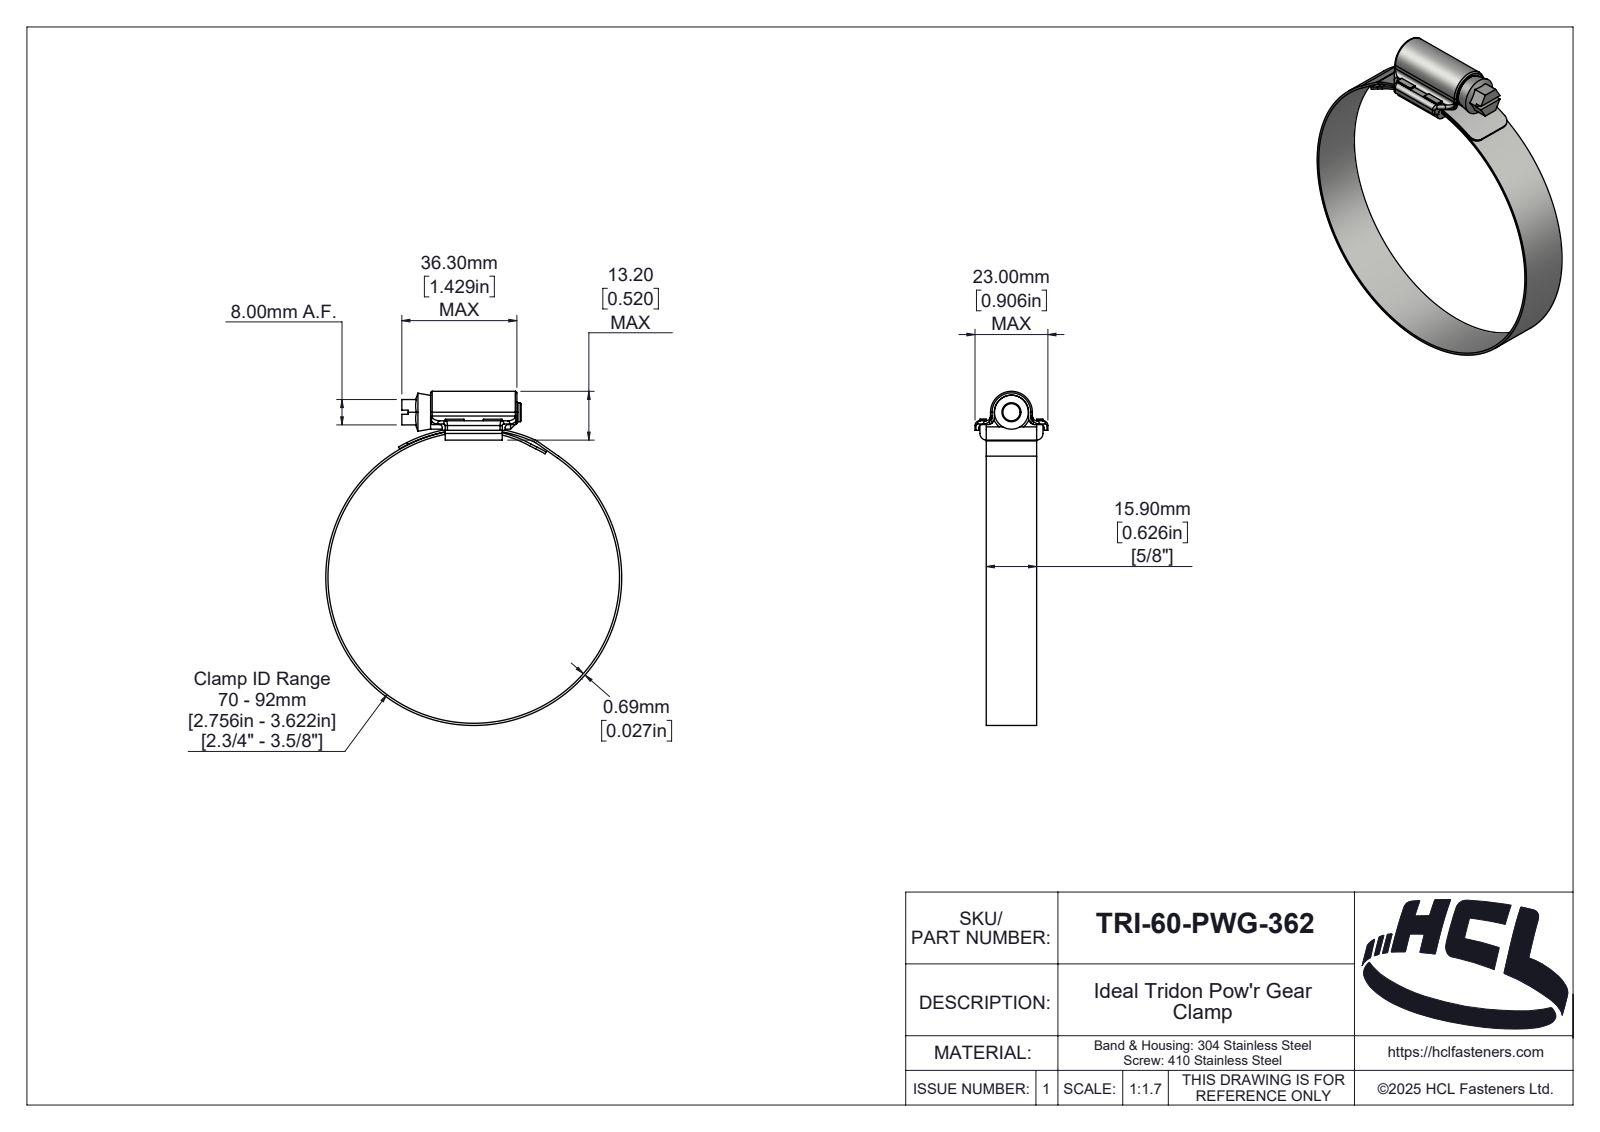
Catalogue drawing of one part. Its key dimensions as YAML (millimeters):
part_name: "TRI-60-PWG-362"
step_written_by: "SolidWorks 2025 (AUTOMOTIVE_DESIGN)"
units: millimeters
bodies: {solids: 4, faces: 268, planar: 87, cylindrical: 102, other: 79}
overall_size: [105.39, 93.38, 23]
volume: 8926
surface_area: 15894
round_holes:
  - {diameter: 92, count: 1}
round_bosses_or_shafts:
  - {diameter: 93.38, count: 1}
  - {diameter: 10.7, count: 1}
  - {diameter: 6, count: 1}
partial_cylinders:
  - {radius: 1, count: 14}
  - {radius: 0.5, count: 4}
  - {radius: 1.5, count: 4}
  - {radius: 2, count: 3}
  - {radius: 0.1, count: 2}
  - {radius: 2.1, count: 2}
  - {radius: 3, count: 2}
  - {radius: 0.46, count: 1}
face_to_face_distances: [2, 15.9, 17.9, 4.9, 0.69, 1.2, 4.55, 3.35, 15.35, 2.55]
